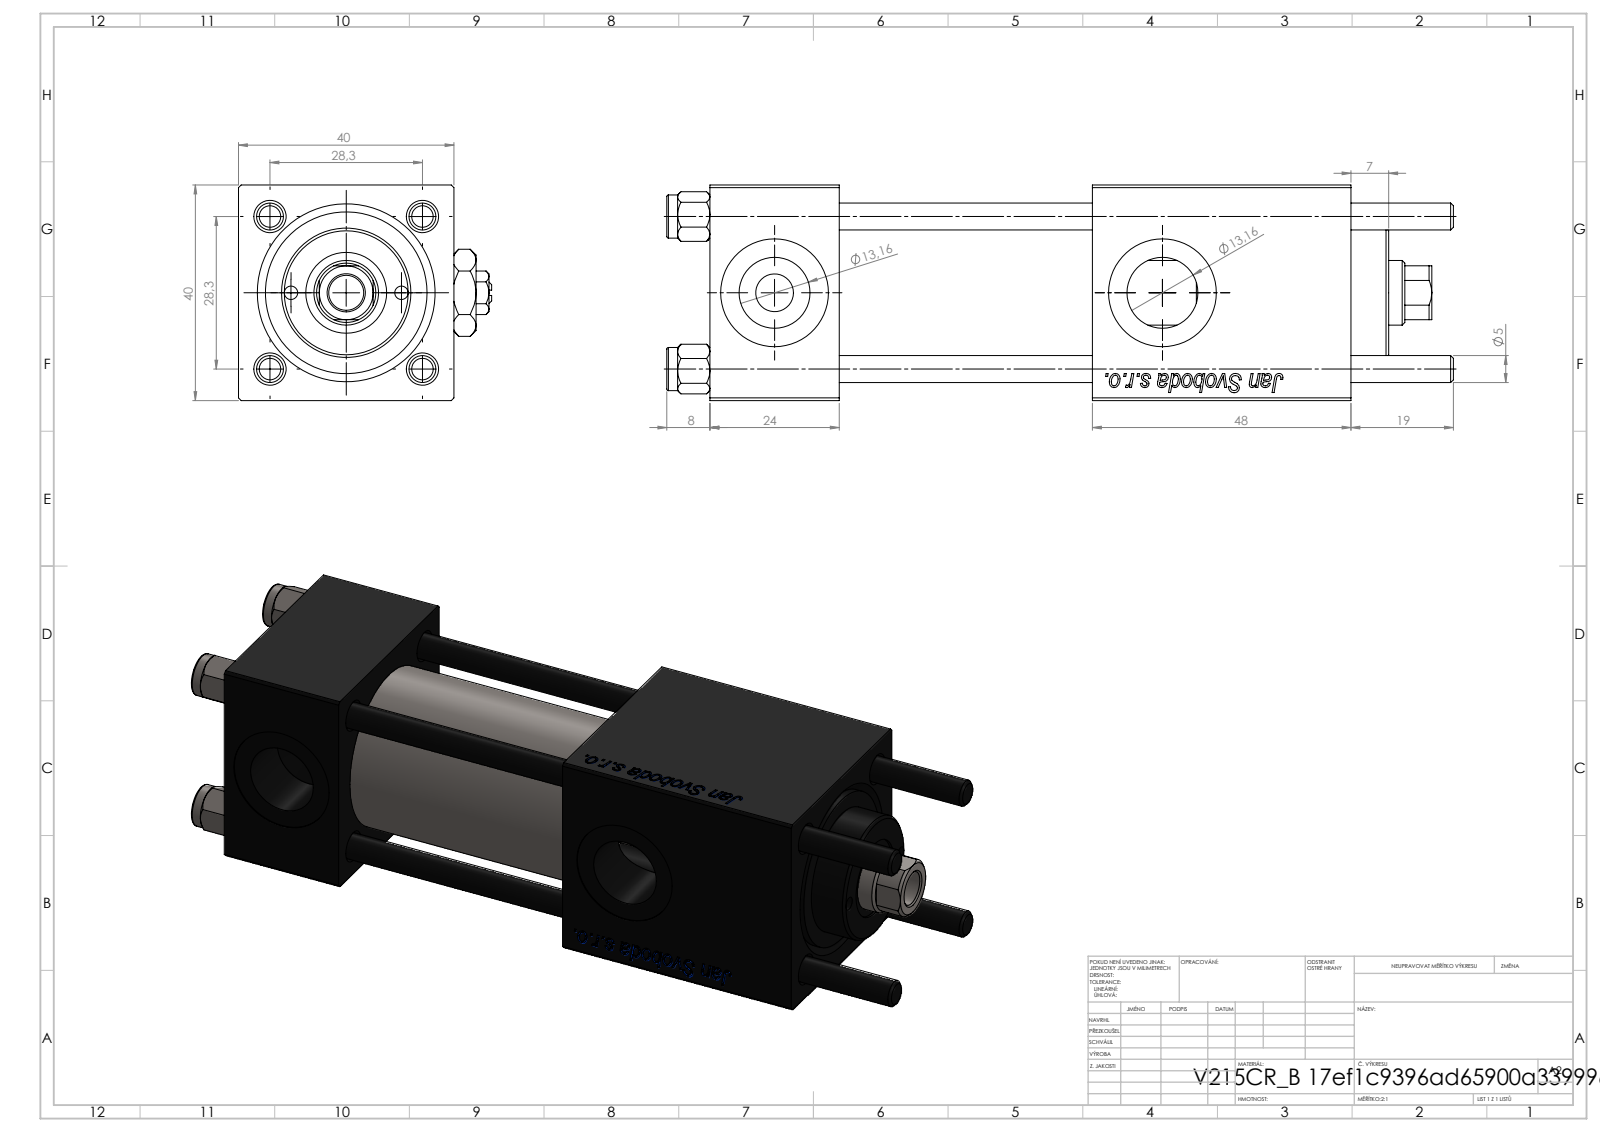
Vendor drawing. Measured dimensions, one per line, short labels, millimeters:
name: V215CR_B-1; V215CR_B_TYCINKA; NUT_M5_B; V215_VC_A (+2 more)
written by: SolidWorks 2019 (CONFIG_CONTROL_DESIGN)
unit: mm
bodies: 12 solids, 1209 faces (455 planar, 86 cylindrical, 668 other)
size: 146 × 47 × 40
volume: 144 116 mm³; area: 59 551 mm²
holes: 4× ⌀5, 3× ⌀20, 2× ⌀2.5, 2× ⌀7, 2× ⌀13.16, 1× ⌀6.5, 1× ⌀12, 1× ⌀15, 1× ⌀25, 1× ⌀30
bosses: 4× ⌀8, 1× ⌀31, 1× ⌀24
rounds: 1× R5.5
face distances: 40, 24, 90.3, 66.3, 47, 71, 19.3, 48, 119, 95
hole spacings: 14.68, 20.01, 28.21, 28.3, 10.25, 40.02, 20.5, 72
